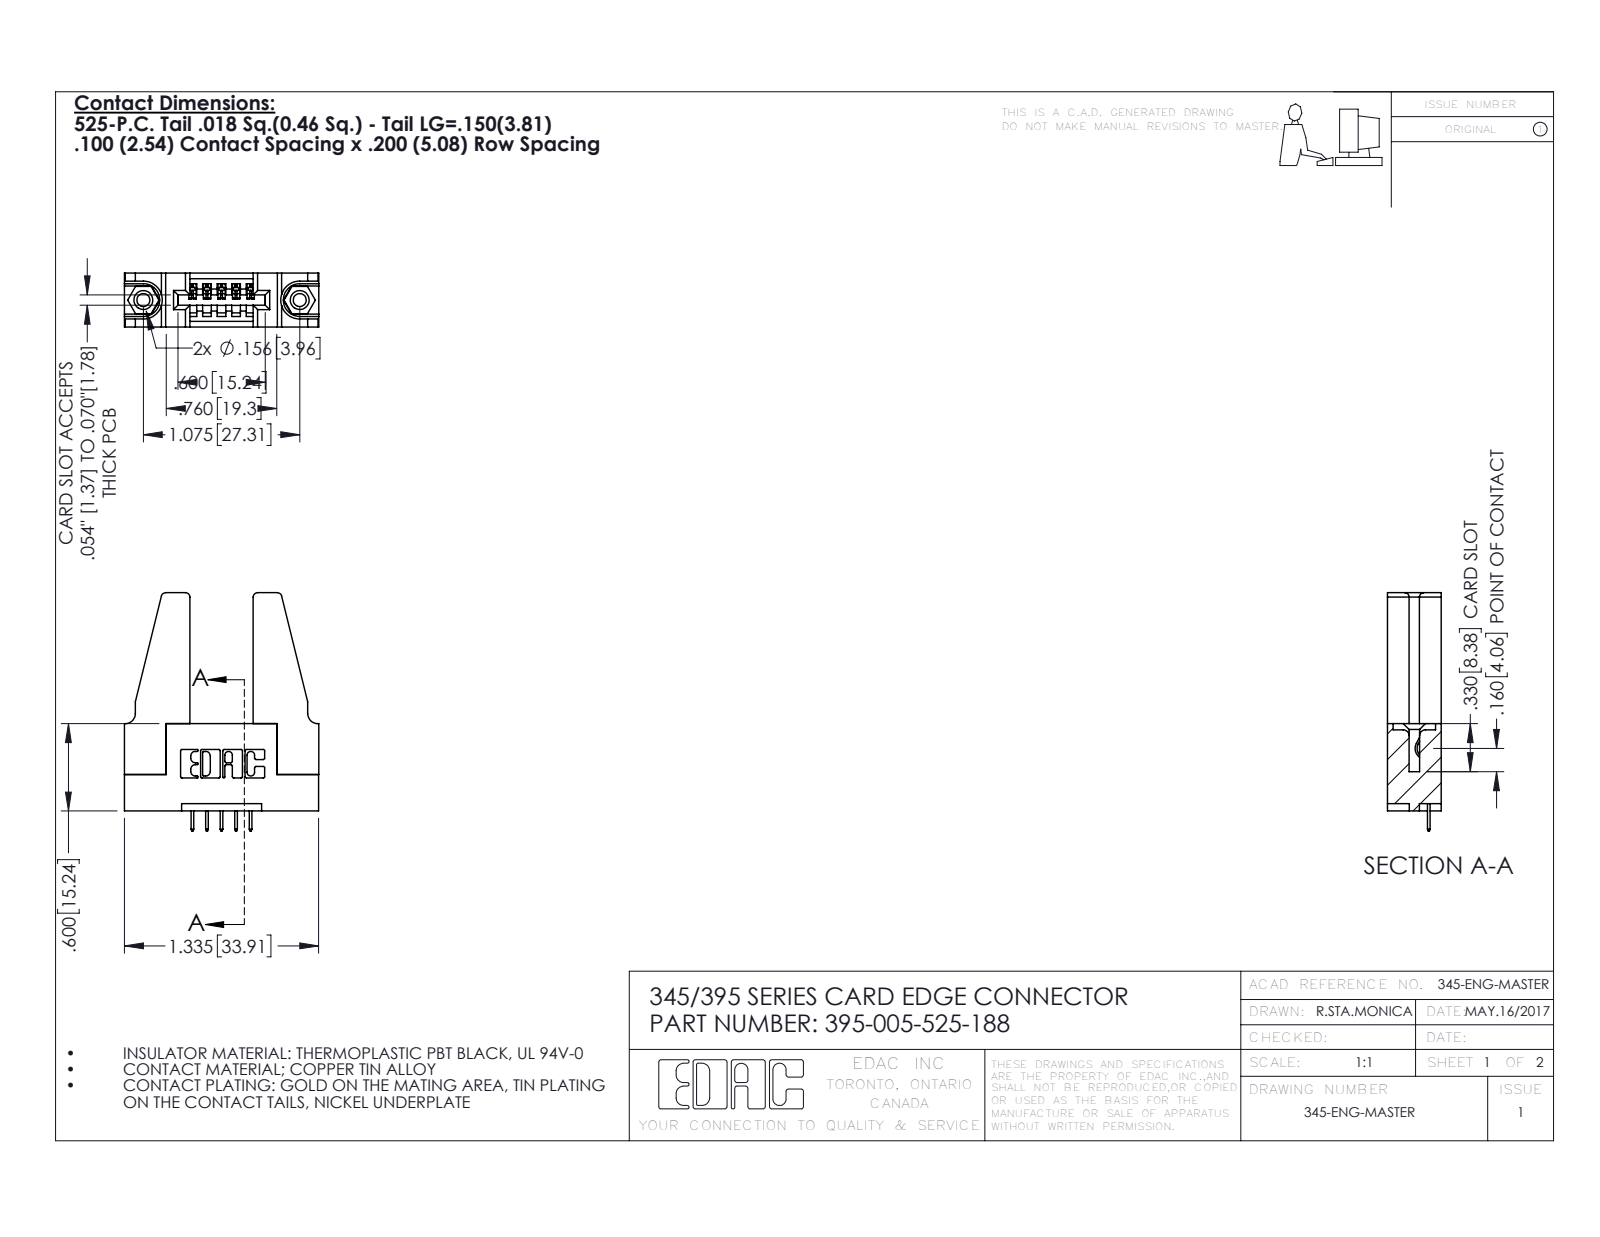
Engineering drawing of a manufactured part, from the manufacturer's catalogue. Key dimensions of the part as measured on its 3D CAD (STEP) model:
Part name (STEP PRODUCT): 345-220-078_345-220-088; 395-005-525-188; 345 Part_Flush Mounting Lugs - 0.156 Dia-TH; 345-250-001_345-250-001-102 (+1 more)
STEP written by: SolidWorks 2020 (CONFIG_CONTROL_DESIGN)
Units: inches
Bodies: 10 solids, 560 faces (382 planar, 162 cylindrical, 16 other)
Overall size (bounding box): 1.637 × 1.336 × 0.37
Volume: 0.375 in³ · Surface area: 9.938 in²
Round holes (diameter × count): ⌀0.089 ×2, ⌀0.125 ×2, ⌀0.156 ×2, ⌀0.064 ×1
Round bosses / shafts (diameter × count): ⌀0.155 ×2
Partial cylindrical surfaces — rounded edges, fillets, slot ends (radius × count): R0.01 ×22, R0.006 ×10, R0.03 ×8, R0.007 ×6, R0.031 ×6, R0.026 ×3, R0.031 ×2, R0.04 ×2
Main face-to-face distances: 0.37, 0.2, 0.072, 0.298, 0.598, 0.25, 0.148, 0.15, 0.35, 0.077
Hole centre spacings: 0.27, 0.847, 1.075
